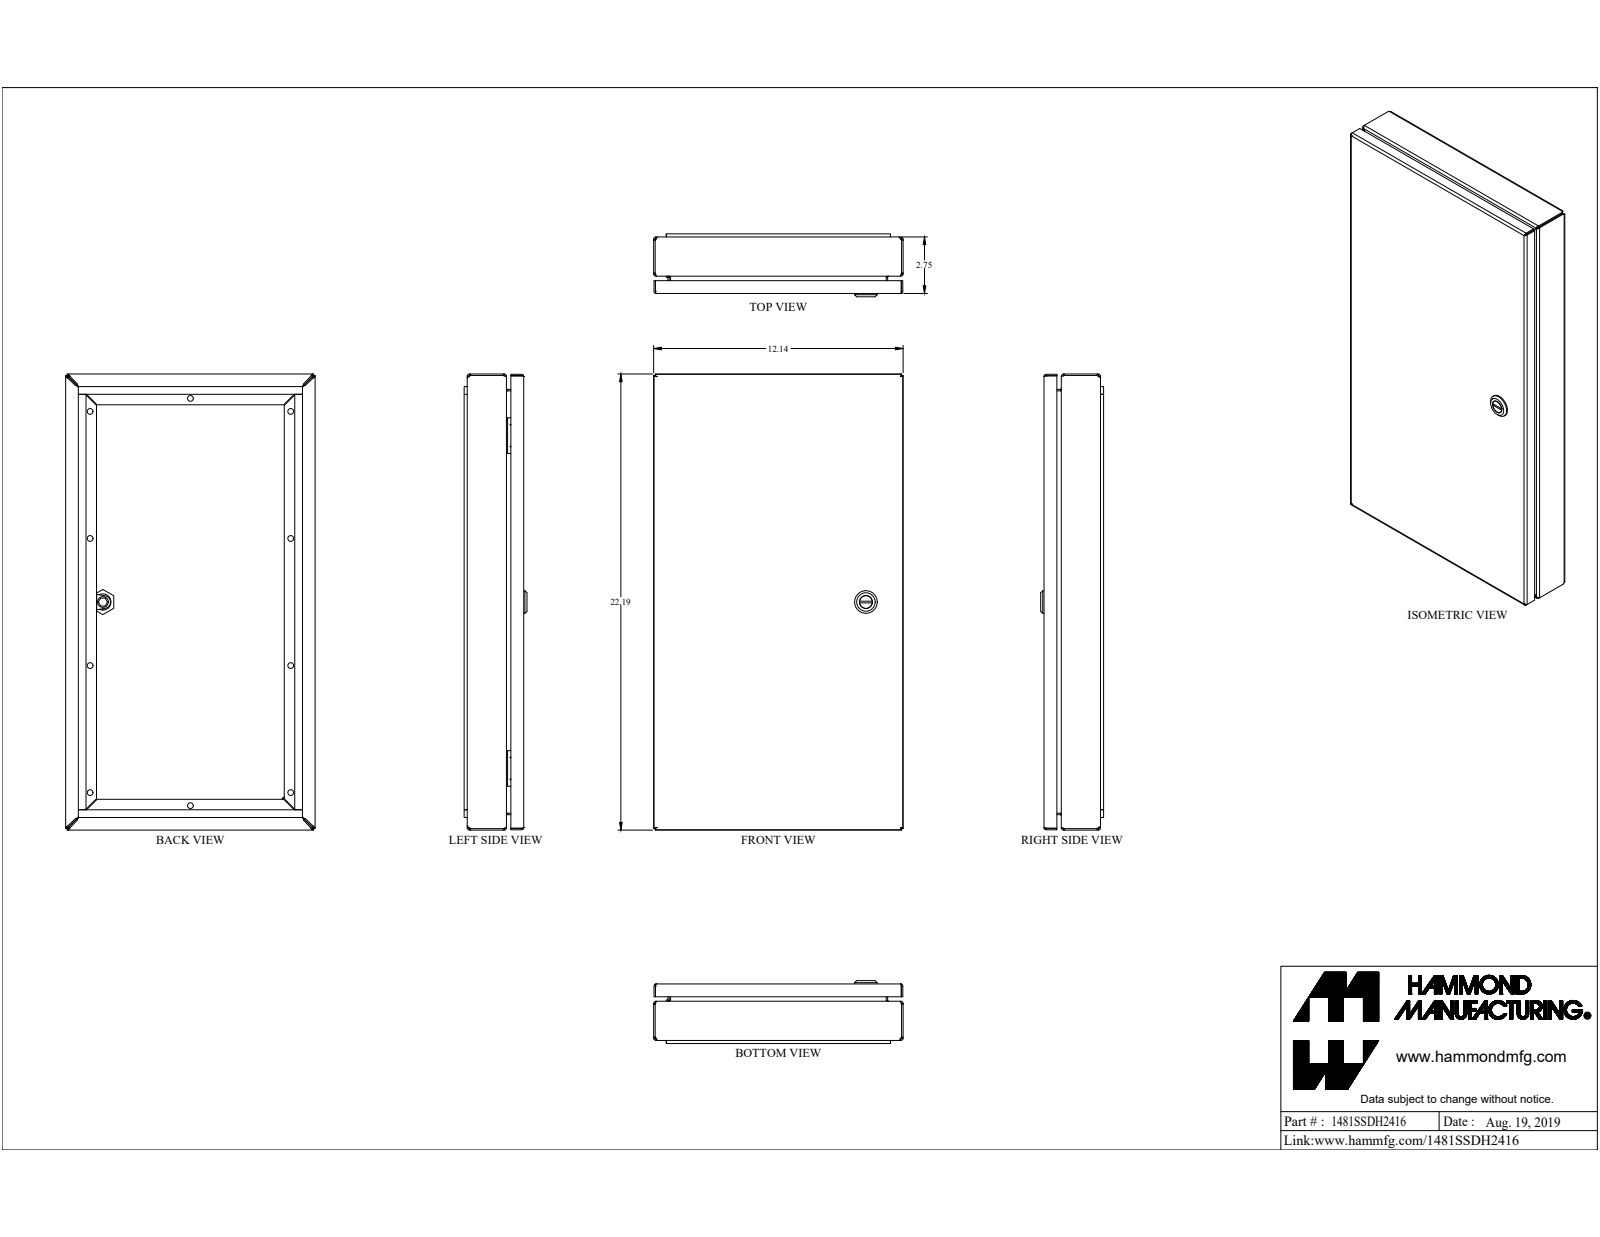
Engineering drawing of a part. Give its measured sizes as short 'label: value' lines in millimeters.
name: 1481SSDH2416
written by: SolidWorks 2019 (CONFIG_CONTROL_DESIGN)
unit: mm
bodies: 24 solids, 620 faces (374 planar, 149 cylindrical, 97 other)
size: 563.6 × 308.4 × 77.7
volume: 935 400 mm³; area: 960 000 mm²
holes: 10× ⌀7.1, 1× ⌀4.4, 1× ⌀5, 1× ⌀6.1, 1× ⌀6.1, 1× ⌀9.8, 1× ⌀12.7, 1× ⌀16, 1× ⌀19.5
bosses: 1× ⌀27.9, 1× ⌀19.9, 1× ⌀15.9, 1× ⌀13.3, 1× ⌀12.1, 1× ⌀10.1, 1× ⌀9, 1× ⌀8
rounds: 28× R0.9, 28× R2.7, 4× R0.2, 4× R1.6, 4× R6.4, 4× R12.7, 2× R3.2, 1× R0.5
face distances: 1.8, 65.5, 21.4, 44.1, 306.5, 67.3, 63.7, 68, 46.6, 2.5
hole spacings: 293.5, 125, 157, 248, 400.2, 502.7, 80.1, 157
